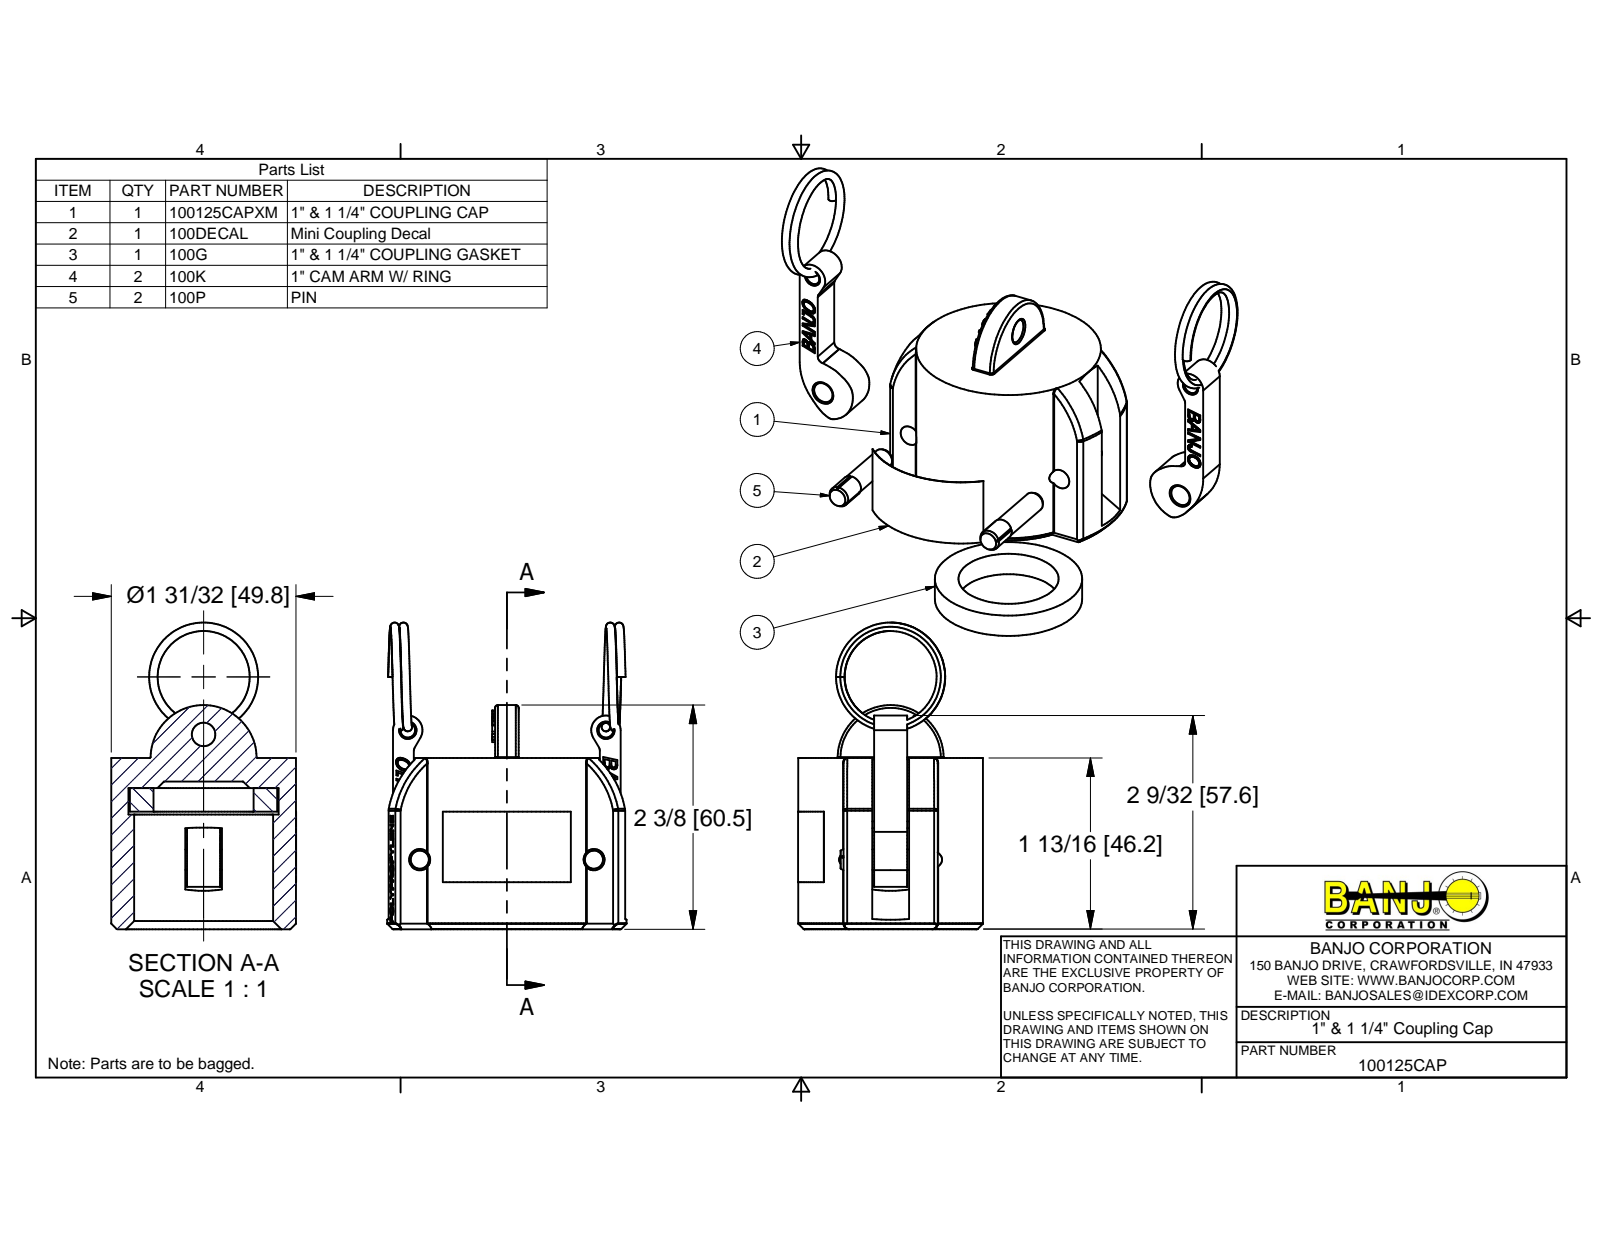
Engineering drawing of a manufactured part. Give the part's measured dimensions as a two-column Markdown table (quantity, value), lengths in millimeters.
| quantity | value |
| --- | --- |
| part name | 100125CAPX; 100125CAPXM; 100XK; 100RING (+6 more) |
| STEP written by | Autodesk Inventor 2015 (AUTOMOTIVE_DESIGN) |
| units | millimeters |
| bodies | 9 solids, 923 faces (468 planar, 84 cylindrical, 371 other) |
| overall size | 82.79 × 64.52 × 49.85 |
| volume | 67 398 mm³ |
| surface area | 31 363 mm² |
| round holes (diameter × count) | 3.96 × 2, 5.56 × 2, 5.71 × 2, 6.35 × 1, 26.99 × 1, 37.47 × 1, 40.49 × 1 |
| round bosses / shafts (diameter × count) | 5.77 × 2, 5.51 × 2, 39.69 × 1 |
| partial cylindrical surfaces (radius × count) | 0.25 × 8, 1.52 × 6, 1.59 × 2, 1.59 × 2, 3.97 × 2, 15.88 × 2, 14.29 × 1, 24.89 × 1 |
| main face-to-face distances | 8.13, 6.35, 7.75, 17.65, 9.9, 8.89, 14.48, 31.75, 38.1, 46.23 |
| hole center spacings | 35.07, 61.12, 46.92, 53.4 |
